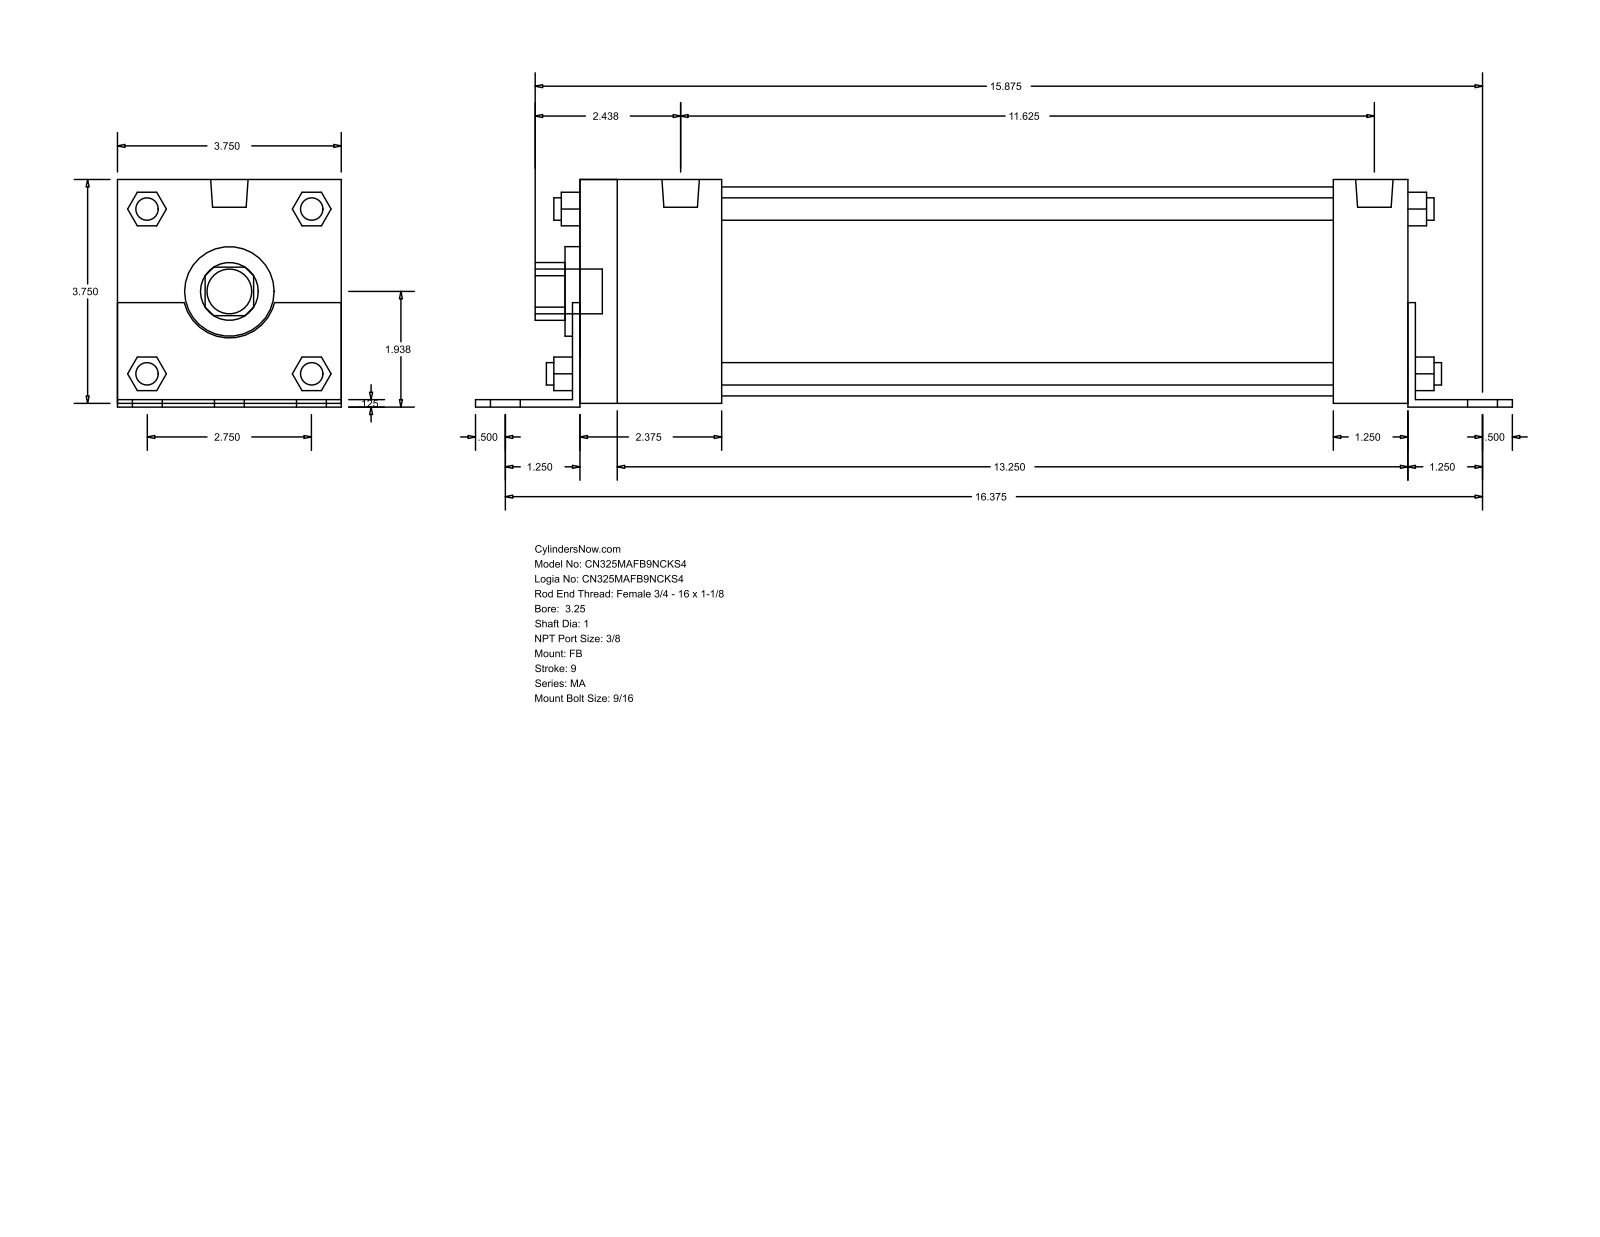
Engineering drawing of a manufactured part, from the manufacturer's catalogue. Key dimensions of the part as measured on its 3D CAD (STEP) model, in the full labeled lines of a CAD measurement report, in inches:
Part name (STEP PRODUCT): MA_FB__0325_1
STEP written by: GSSL Pune (CONFIG_CONTROL_DESIGN)
Units: inches
Bodies: 0 solids, 140 faces (105 planar, 35 cylindrical, 0 other)
Overall size (bounding box): 17.375 × 3.813 × 3.75
Round holes (diameter × count): ⌀1 ×1, ⌀1.5 ×1, ⌀3.5 ×1
Round bosses / shafts (diameter × count): ⌀0.563 ×6, ⌀0.437 ×4, ⌀0.375 ×4, ⌀0.627 ×2, ⌀0.75 ×1
Partial cylindrical surfaces — rounded edges, fillets, slot ends (radius × count): R0.484 ×1, R0.78 ×1
Main face-to-face distances: 3.75, 0.125, 0.063, 3.812, 0.062, 3.687, 14, 13.875, 14.125, 12.75
